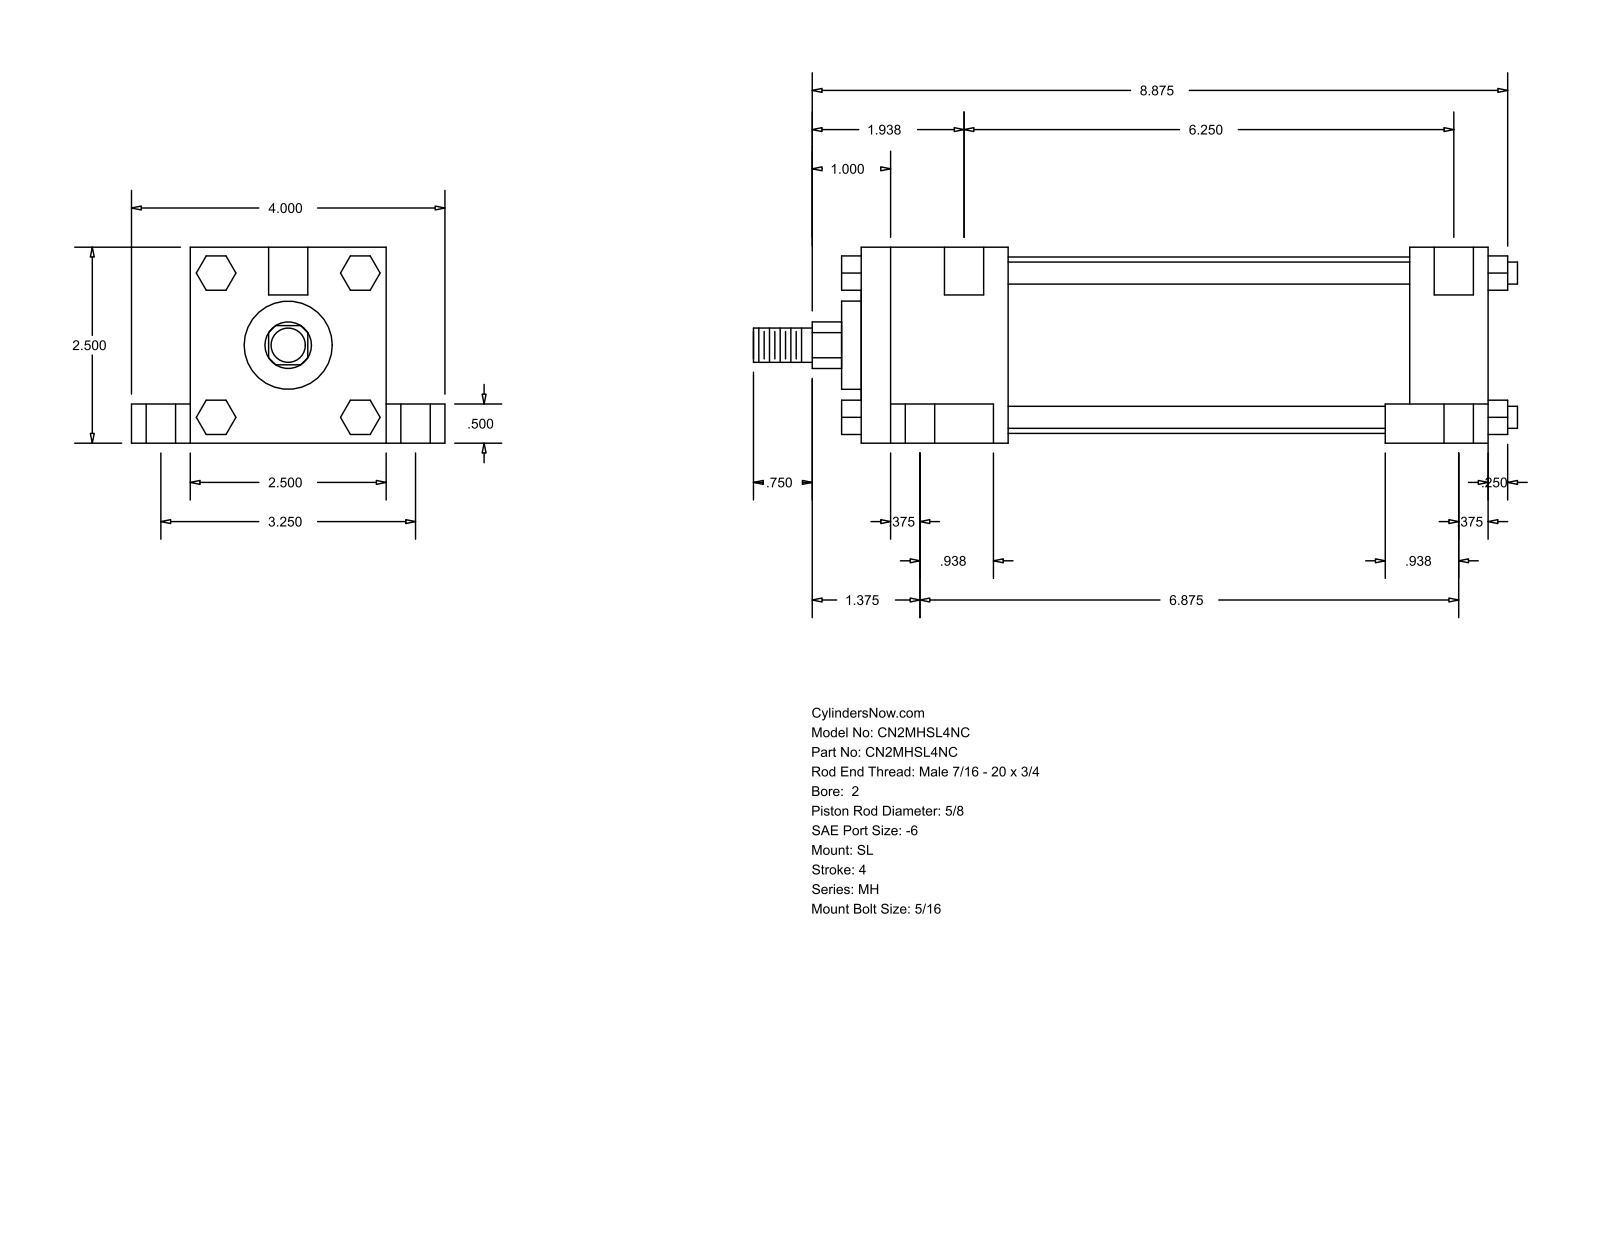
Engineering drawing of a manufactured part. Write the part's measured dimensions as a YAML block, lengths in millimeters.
part_name: "MH_SL__0200_0.625"
step_written_by: "GSSL Pune (CONFIG_CONTROL_DESIGN)"
units: millimeters
bodies: {solids: 0, faces: 148, planar: 112, cylindrical: 36, other: 0}
overall_size: [247.65, 101.6, 63.5]
round_holes:
  - {diameter: 5.56, count: 4}
  - {diameter: 9.53, count: 4}
  - {diameter: 15.88, count: 4}
  - {diameter: 12.7, count: 2}
round_bosses_or_shafts:
  - {diameter: 7.14, count: 4}
  - {diameter: 57.15, count: 1}
  - {diameter: 28.57, count: 1}
  - {diameter: 15.88, count: 1}
  - {diameter: 11.11, count: 1}
partial_cylinders:
  - {radius: 7.54, count: 1}
face_to_face_distances: [63.5, 203.19, 12.7, 19.05, 82.55, 50.8, 177.8, 25.39, 47.62, 130.18]
hole_center_spacings: [41.3, 42.36, 43.67, 82.54, 165.57, 166.69, 170.18, 174.63]
